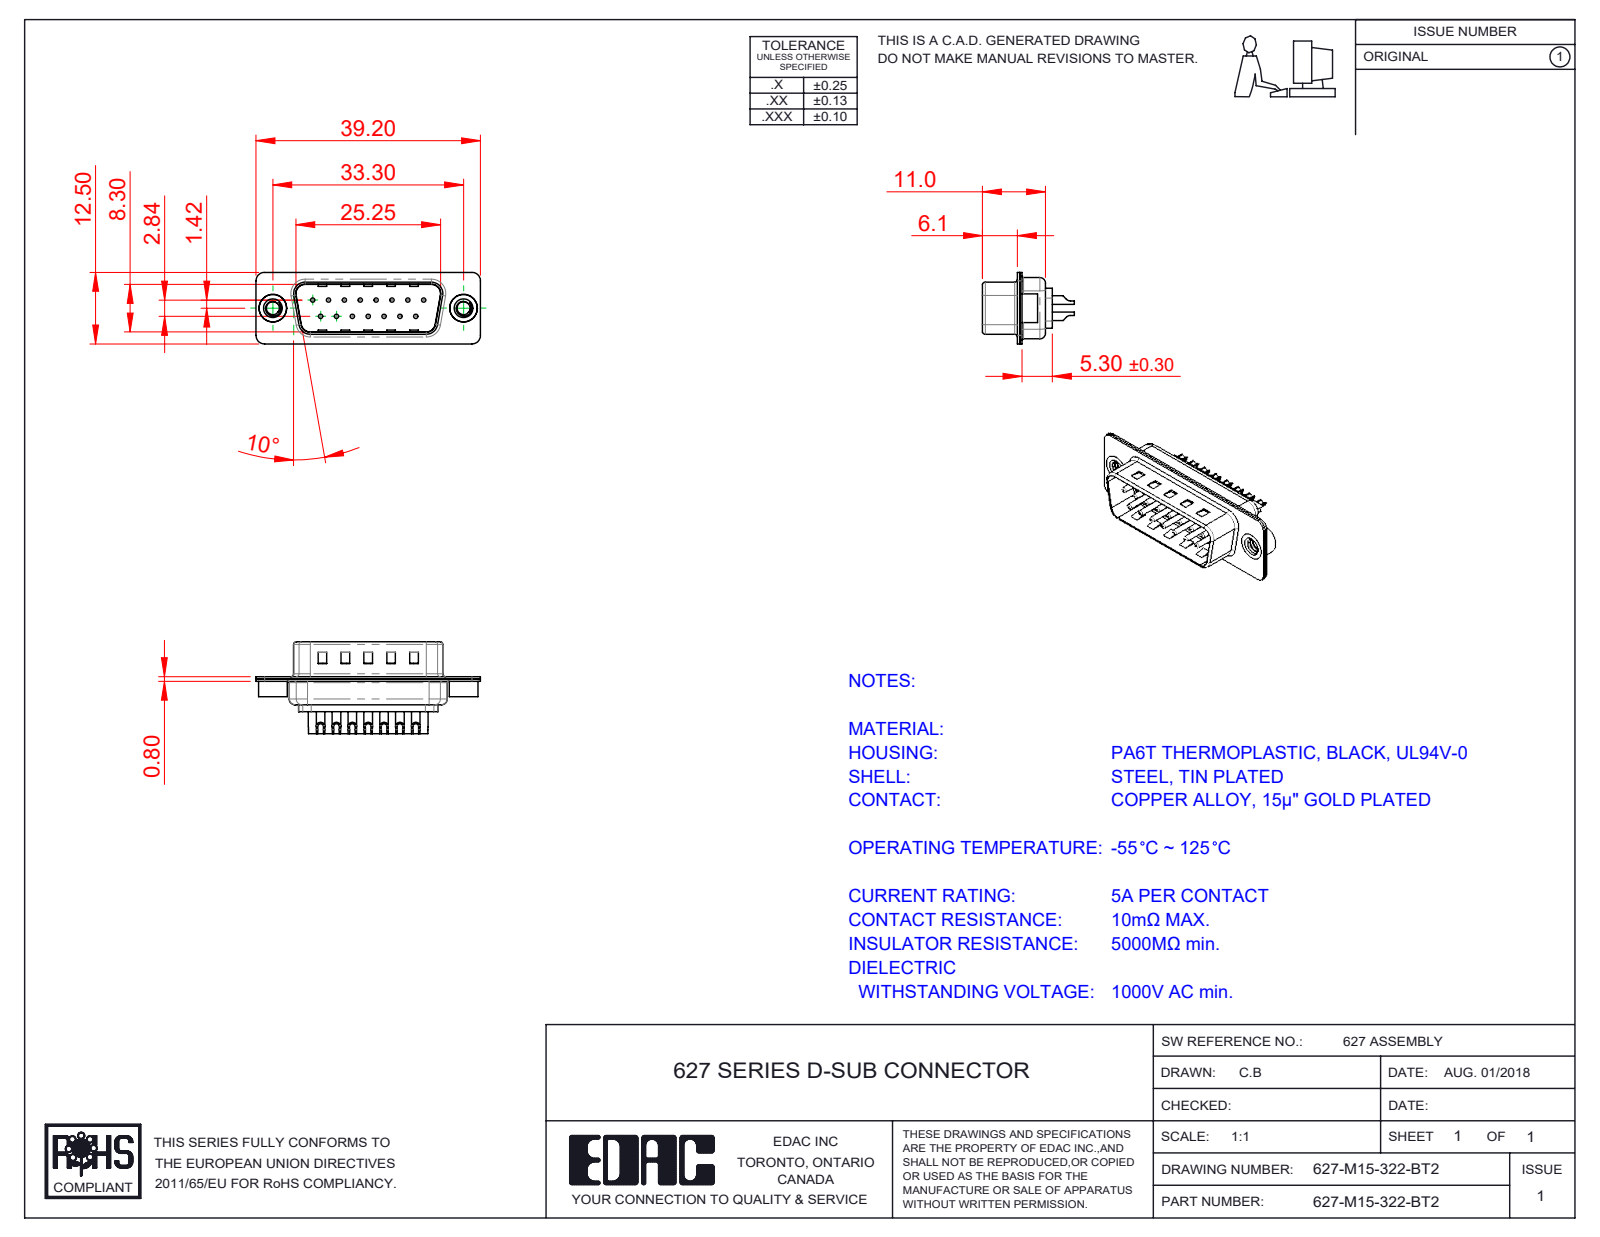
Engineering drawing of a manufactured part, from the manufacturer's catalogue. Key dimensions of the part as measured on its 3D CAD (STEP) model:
Part name (STEP PRODUCT): 627-M15-322-BT2; 627M Contact Row 1_22; 627M Shell Rear_15 Contacts; 627M Shell Front_15 Contacts (+3 more)
STEP written by: SolidWorks 2020 (CONFIG_CONTROL_DESIGN)
Units: millimetres
Bodies: 20 solids, 895 faces (274 planar, 373 cylindrical, 248 other)
Overall size (bounding box): 39.2 × 16.05 × 12.5
Volume: 1 878 mm³ · Surface area: 4 949 mm²
Round holes (diameter × count): ⌀0.75 ×15, ⌀1 ×15, ⌀1.6 ×15, ⌀2 ×15, ⌀2.26 ×2, ⌀4 ×2, ⌀4.8 ×2
Round bosses / shafts (diameter × count): ⌀1.5 ×15, ⌀5 ×2, ⌀4.9 ×2
Partial cylindrical surfaces — rounded edges, fillets, slot ends (radius × count): R1.5 ×16, R2 ×12, R0.5 ×8, R1.6 ×8, R1 ×6, R0.25 ×4, R0.6 ×4, R0.65 ×4
Main face-to-face distances: 0.4, 0.8, 9.5, 9.1, 8.7, 9.9, 1.2, 0.75, 0.35, 6.1
Hole centre spacings: 3.16, 2.77, 5.54, 8.31, 11.08, 5.03, 5.04, 7.48
